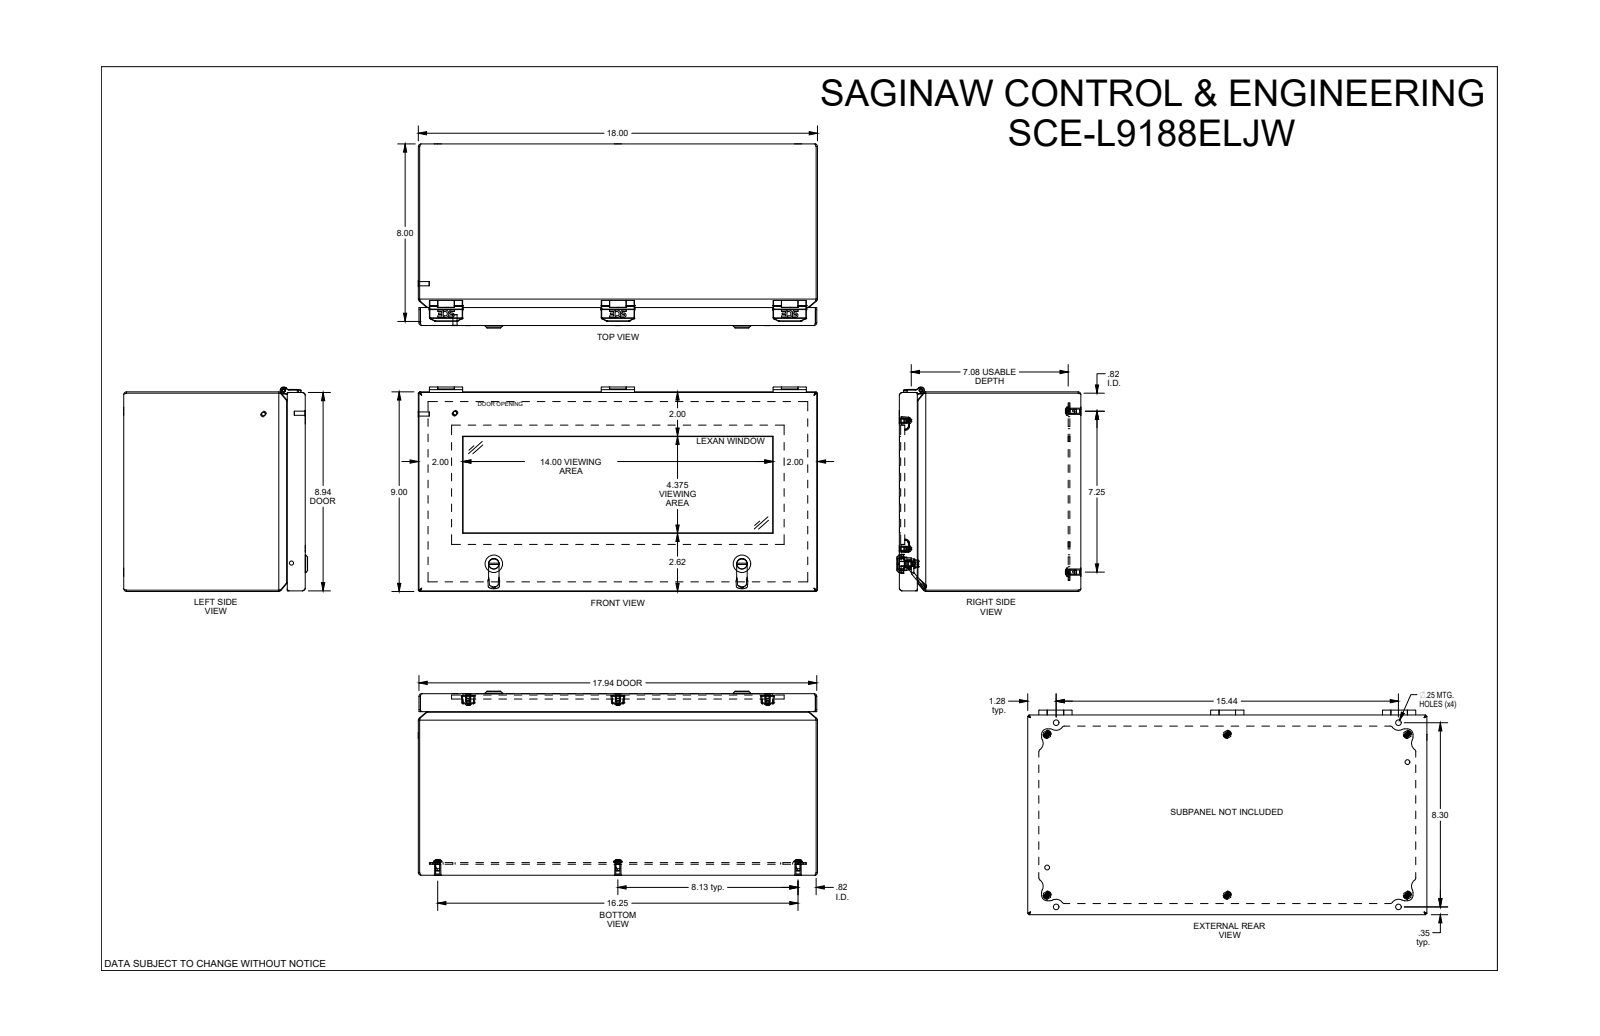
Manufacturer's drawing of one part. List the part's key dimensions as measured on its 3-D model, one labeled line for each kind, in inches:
Part name (STEP PRODUCT): SCE-L9188ELJWSS
STEP written by: SolidWorks 2022 (AUTOMOTIVE_DESIGN)
Units: inches
Bodies: 64 solids, 2369 faces (1177 planar, 614 cylindrical, 578 other)
Overall size (bounding box): 18.004 × 9.22 × 8.296
Volume: 76.99 in³ · Surface area: 2 028 in²
Round holes (diameter × count): ⌀0.138 ×6, ⌀0.156 ×6, ⌀0.19 ×6, ⌀0.213 ×6, ⌀0.25 ×6, ⌀0.284 ×6, ⌀0.164 ×3, ⌀0.174 ×3, ⌀0.266 ×3, ⌀0.338 ×3, ⌀0.2 ×2, ⌀0.218 ×2
Round bosses / shafts (diameter × count): ⌀0.188 ×8, ⌀0.373 ×6, ⌀0.28 ×6, ⌀0.262 ×6, ⌀0.212 ×6, ⌀0.26 ×3, ⌀0.15 ×3, ⌀0.788 ×2
Partial cylindrical surfaces — rounded edges, fillets, slot ends (radius × count): R0.008 ×48, R0.02 ×44, R0.05 ×36, R0.125 ×13, R0.25 ×13, R0.01 ×12, R0.062 ×12, R0.06 ×8
Main face-to-face distances: 0.059, 8.941, 0.571, 0.512, 0.496, 0.437, 0.075, 8.125, 7.554, 8.066
Hole centre spacings: 7.75, 8.125, 10.889, 15.5, 6.75, 6.763, 7.25, 7.251
